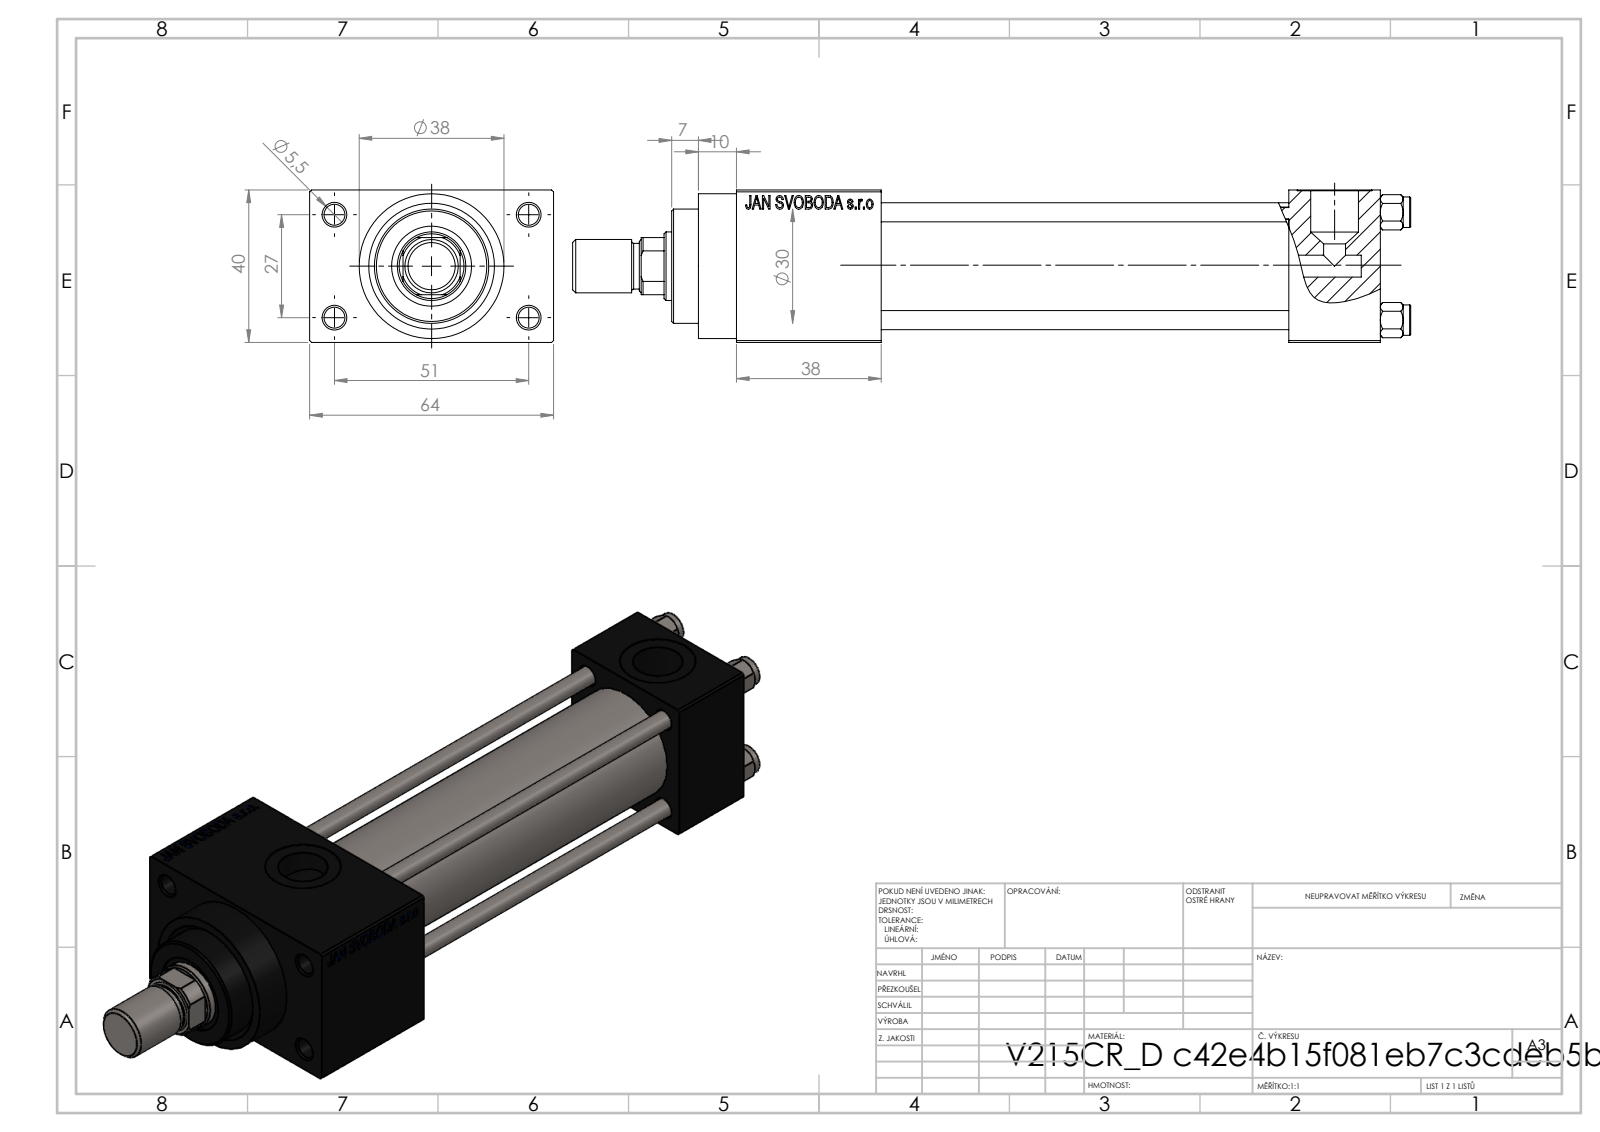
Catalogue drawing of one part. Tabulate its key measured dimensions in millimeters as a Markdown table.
| quantity | value |
| --- | --- |
| part name | NUT_M5_D; V215CR_D_Body; V215_VC_A; ROD_END_AH (+2 more) |
| STEP written by | SolidWorks 2019 (CONFIG_CONTROL_DESIGN) |
| units | millimeters |
| bodies | 12 solids, 1116 faces (499 planar, 91 cylindrical, 526 other) |
| overall size | 220 × 64 × 40 |
| volume | 219 160 mm³ |
| surface area | 82 979 mm² |
| round holes (diameter × count) | 5 × 4, 5.5 × 4, 20 × 3, 7 × 2, 13.16 × 2, 8.5 × 1, 18 × 1, 21 × 1, 25 × 1, 30 × 1 |
| round bosses / shafts (diameter × count) | 8 × 4, 38 × 1, 31 × 1, 14 × 1, 12 × 1 |
| partial cylindrical surfaces (radius × count) | 8.5 × 1 |
| main face-to-face distances | 40, 12, 52, 107, 24, 131, 64, 38, 169, 145 |
| hole center spacings | 11.37, 20.01, 28.3, 28.85, 29.89, 39.66, 48.34, 27 |
